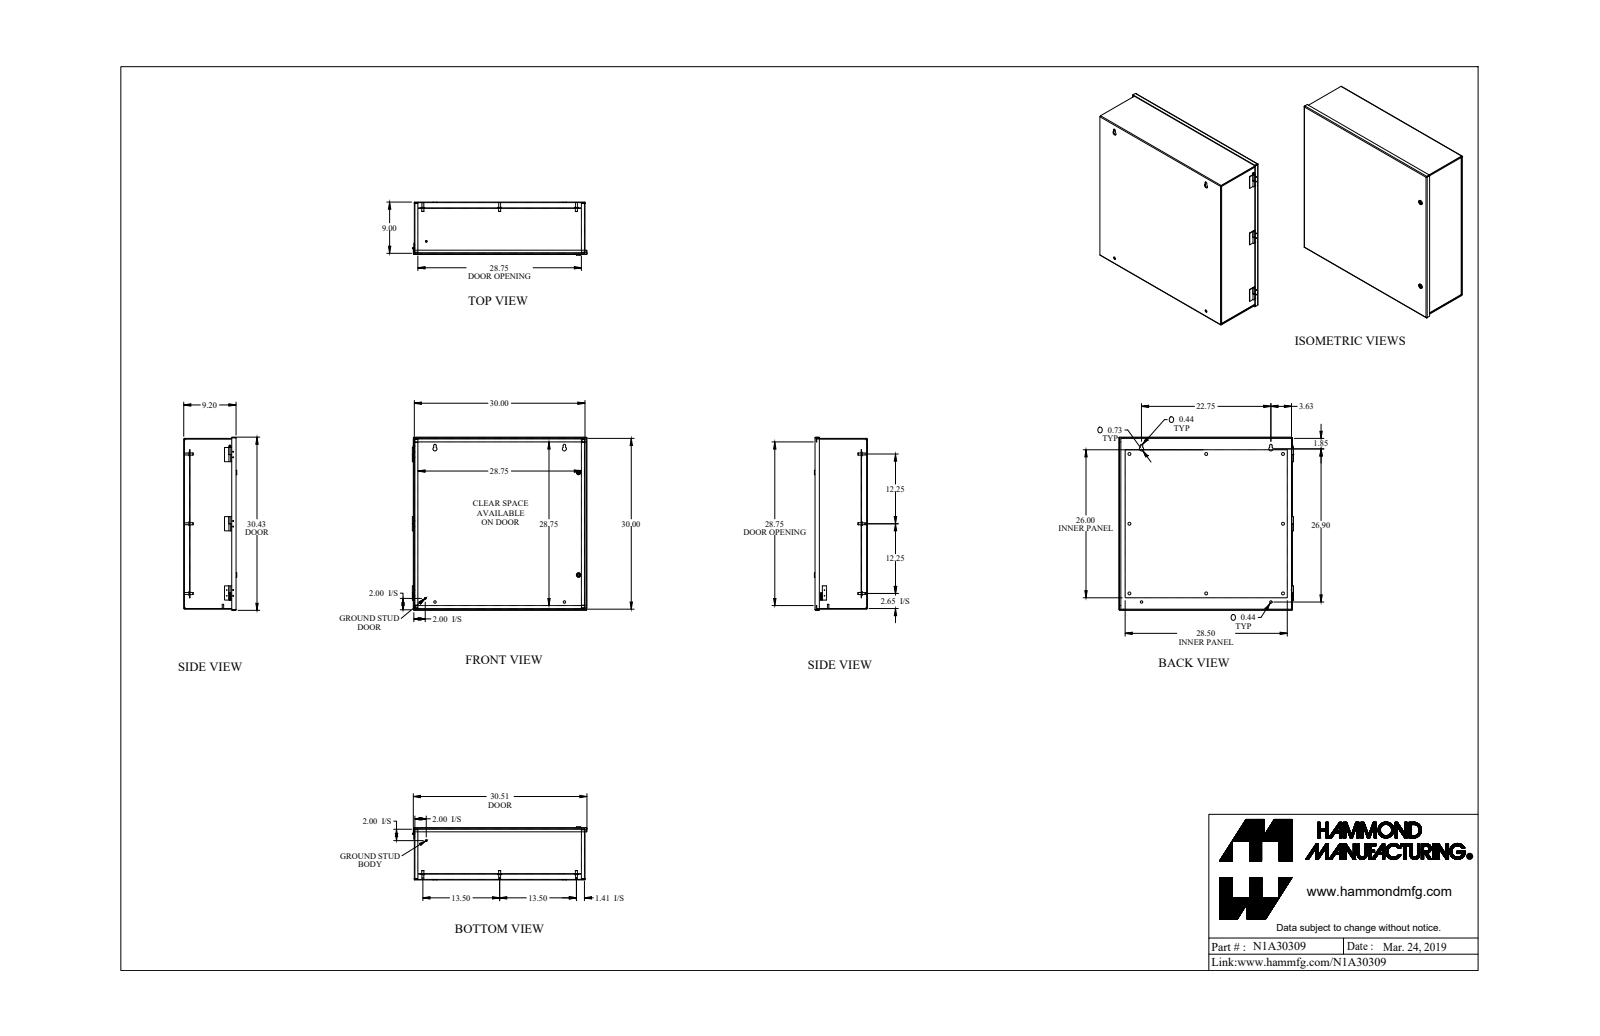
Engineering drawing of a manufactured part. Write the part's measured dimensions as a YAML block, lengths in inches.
part_name: "N1A30309"
step_written_by: "SolidWorks 2018 (AUTOMOTIVE_DESIGN)"
units: inches
bodies: {solids: 36, faces: 807, planar: 442, cylindrical: 285, other: 80}
overall_size: [30.681, 30.43, 9.322]
volume: 349.3
surface_area: 7767
round_holes:
  - {diameter: 0.14, count: 12}
  - {diameter: 0.5, count: 8}
  - {diameter: 0.307, count: 4}
  - {diameter: 0.445, count: 4}
  - {diameter: 0.734, count: 3}
  - {diameter: 0.437, count: 2}
  - {diameter: 0.516, count: 2}
  - {diameter: 0.17, count: 1}
  - {diameter: 0.187, count: 1}
round_bosses_or_shafts:
  - {diameter: 0.128, count: 12}
  - {diameter: 0.375, count: 9}
  - {diameter: 0.65, count: 8}
  - {diameter: 0.33, count: 8}
  - {diameter: 1, count: 4}
  - {diameter: 0.788, count: 2}
  - {diameter: 0.535, count: 2}
  - {diameter: 0.496, count: 2}
partial_cylinders:
  - {radius: 0.048, count: 16}
  - {radius: 0.143, count: 16}
  - {radius: 0.219, count: 3}
  - {radius: 0.06, count: 2}
  - {radius: 0.125, count: 2}
  - {radius: 0.153, count: 2}
  - {radius: 0.315, count: 2}
  - {radius: 0.03, count: 1}
face_to_face_distances: [0.095, 0.095, 9.01, 9.105, 9.105, 9.2, 29.905, 0.072, 0.937, 1.104]
hole_center_spacings: [1, 1.119, 12.25, 13.5, 18.23, 24.34, 27.973, 29.649]
